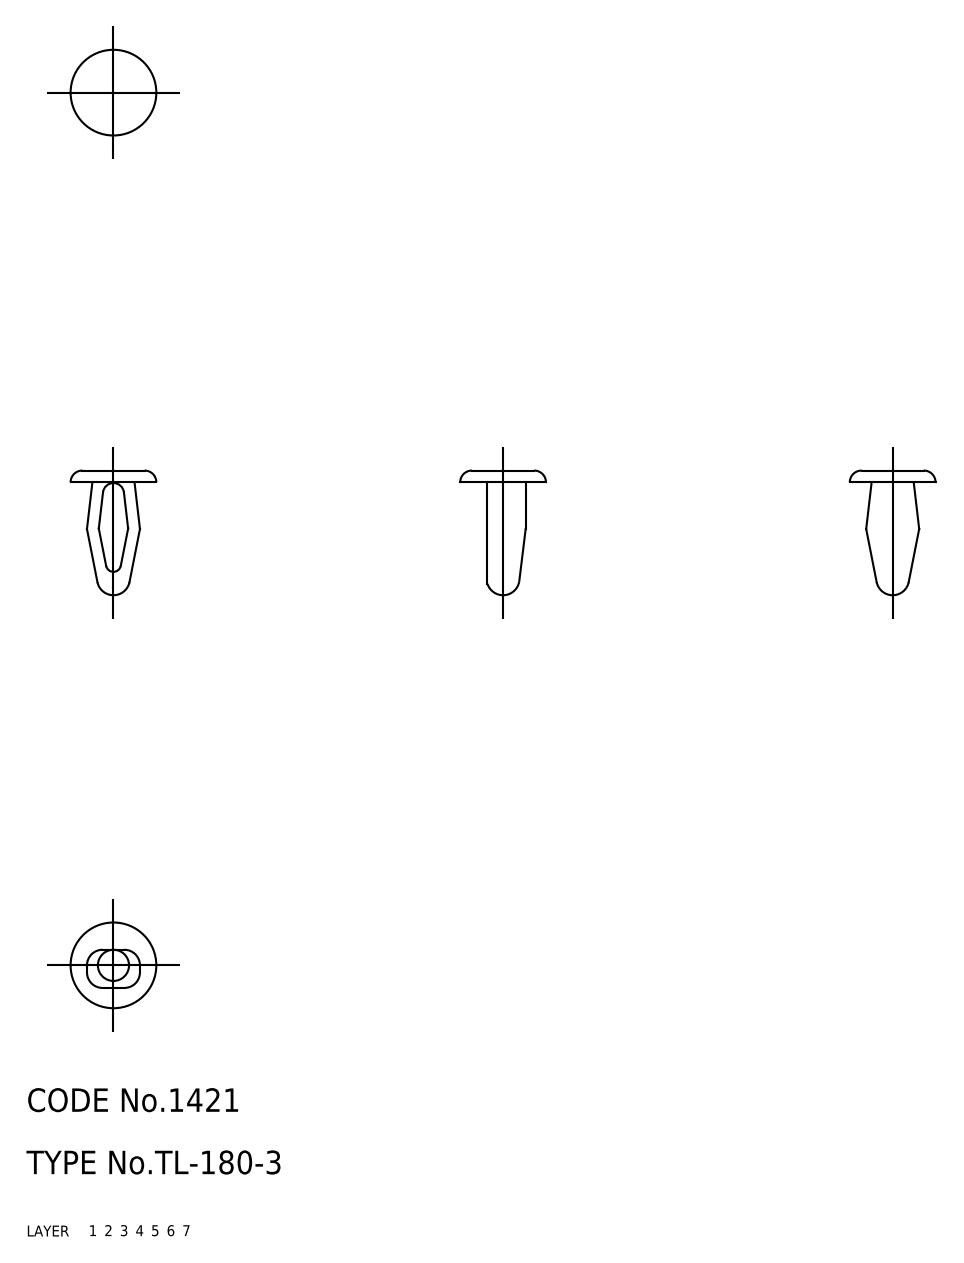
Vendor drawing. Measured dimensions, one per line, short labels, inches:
name: fastener
written by: CADfix (AUTOMOTIVE_DESIGN)
unit: in
bodies: 1 solid, 34 faces (0 planar, 0 cylindrical, 34 other)
size: 0.63 × 0.433 × 0.433
volume: 0.021 in³; area: 0.797 in²
